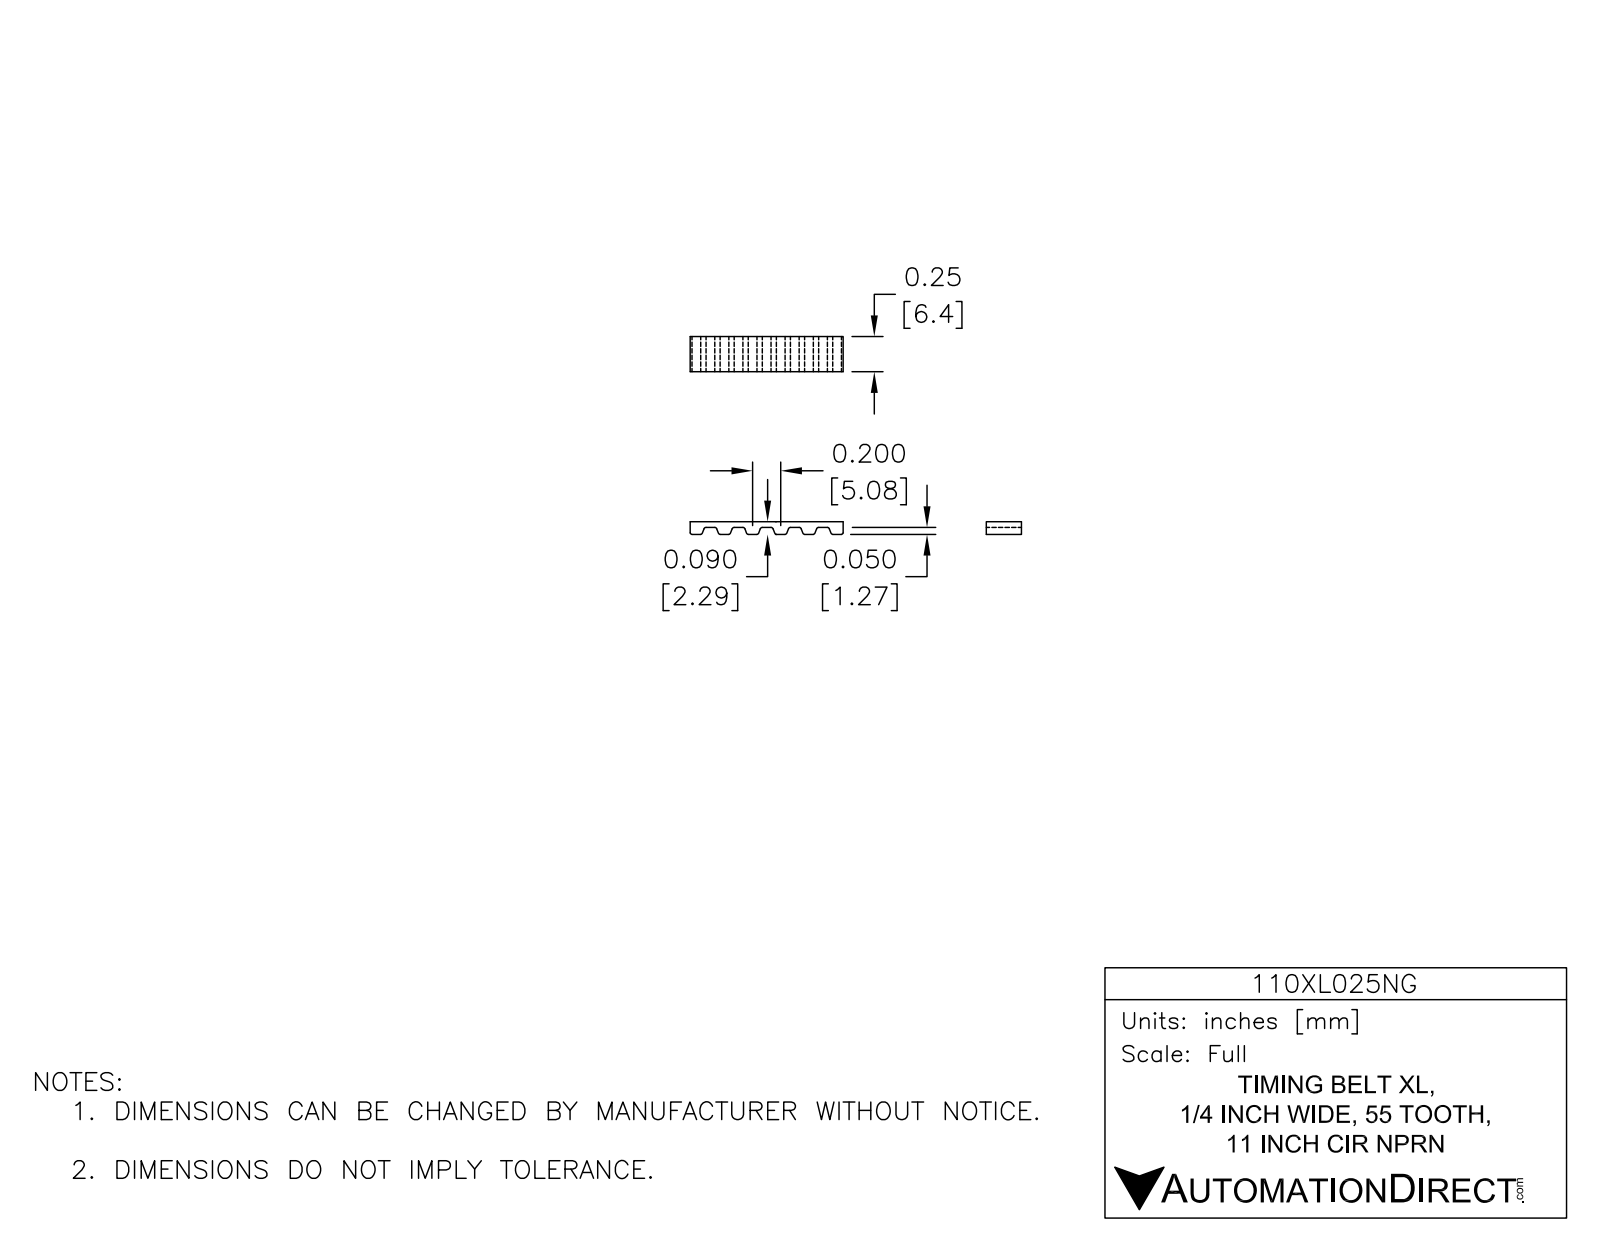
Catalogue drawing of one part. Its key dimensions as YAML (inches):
part_name: "110XL025NG"
step_written_by: "SolidWorks 2014 (AUTOMOTIVE_DESIGN)"
units: inches
bodies: {solids: 1, faces: 478, planar: 178, cylindrical: 300, other: 0}
overall_size: [3.788, 3, 0.25]
volume: 0.149
surface_area: 7.386
partial_cylinders:
  - {radius: 0.015, count: 220}
  - {radius: 1.46, count: 2}
  - {radius: 1.5, count: 2}
face_to_face_distances: [0.25, 3, 0.04, 2.96, 2.92, 0.177, 1.072, 0.354, 0.895, 0.354]
